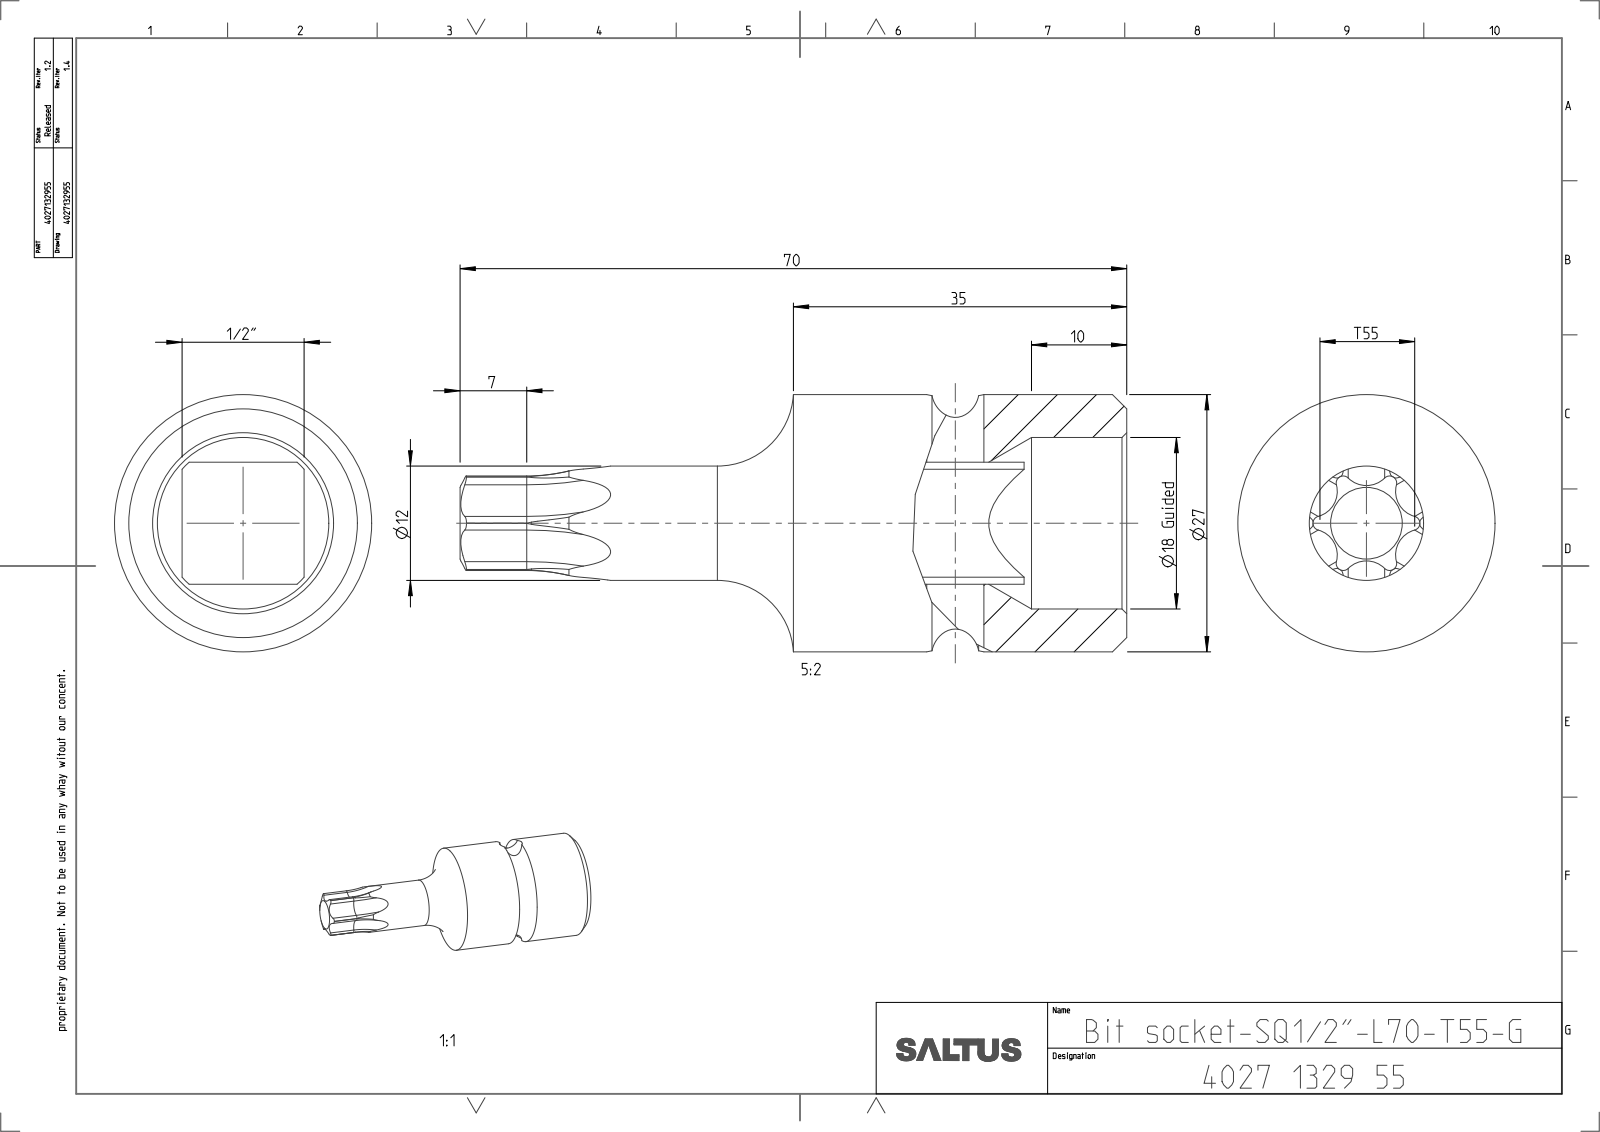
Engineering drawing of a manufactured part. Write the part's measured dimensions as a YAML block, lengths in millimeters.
part_name: "4027132955"
step_written_by: "CREO PARAMETRIC BY PTC INC, 2022414 (CONFIG_CONTROL_DESIGN)"
units: millimeters
bodies: {solids: 1, faces: 83, planar: 7, cylindrical: 40, other: 36}
overall_size: [70, 27, 27]
volume: 17790
surface_area: 6701
round_holes:
  - {diameter: 6, count: 1}
  - {diameter: 18, count: 1}
round_bosses_or_shafts:
  - {diameter: 27, count: 1}
  - {diameter: 12, count: 1}
partial_cylinders:
  - {radius: 0.73, count: 12}
  - {radius: 2.71, count: 6}
  - {radius: 5.61, count: 1}
  - {radius: 8.55, count: 1}
face_to_face_distances: [12.82, 26, 70, 44]
